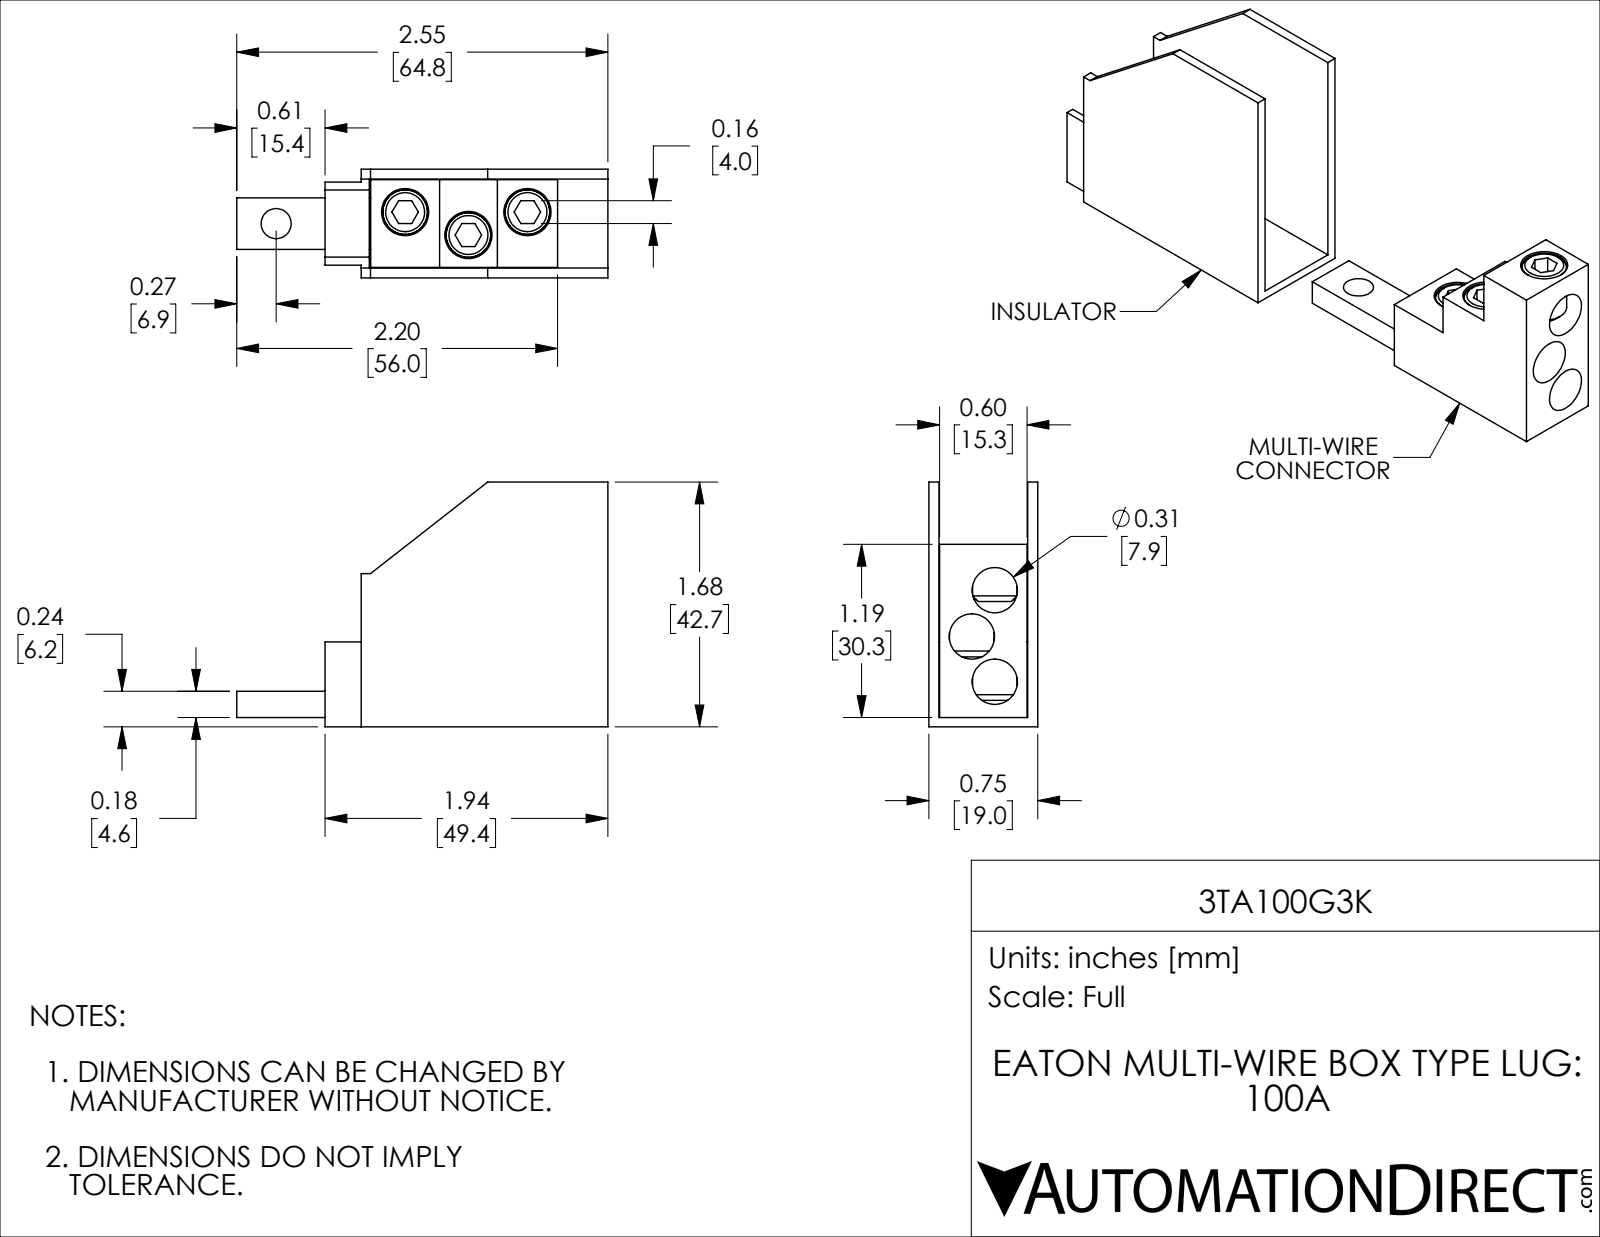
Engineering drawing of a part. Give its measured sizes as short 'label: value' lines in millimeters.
name: 3TA100G3K
written by: SolidWorks 2019 (CONFIG_CONTROL_DESIGN)
unit: mm
bodies: 5 solids, 109 faces (71 planar, 20 cylindrical, 18 other)
size: 64.8 × 42.7 × 19
volume: 16 172 mm³; area: 15 894 mm²
holes: 3× ⌀7.83, 3× ⌀7.9, 1× ⌀5.25
bosses: 3× ⌀7.8
face distances: 17.25, 1.75, 19, 15.5, 1.85, 15.4, 17.15, 1.6, 15.3, 3.25
hole spacings: 8.85, 9.02, 11.05, 11.75, 15.99, 21.35, 22.61, 33.63
